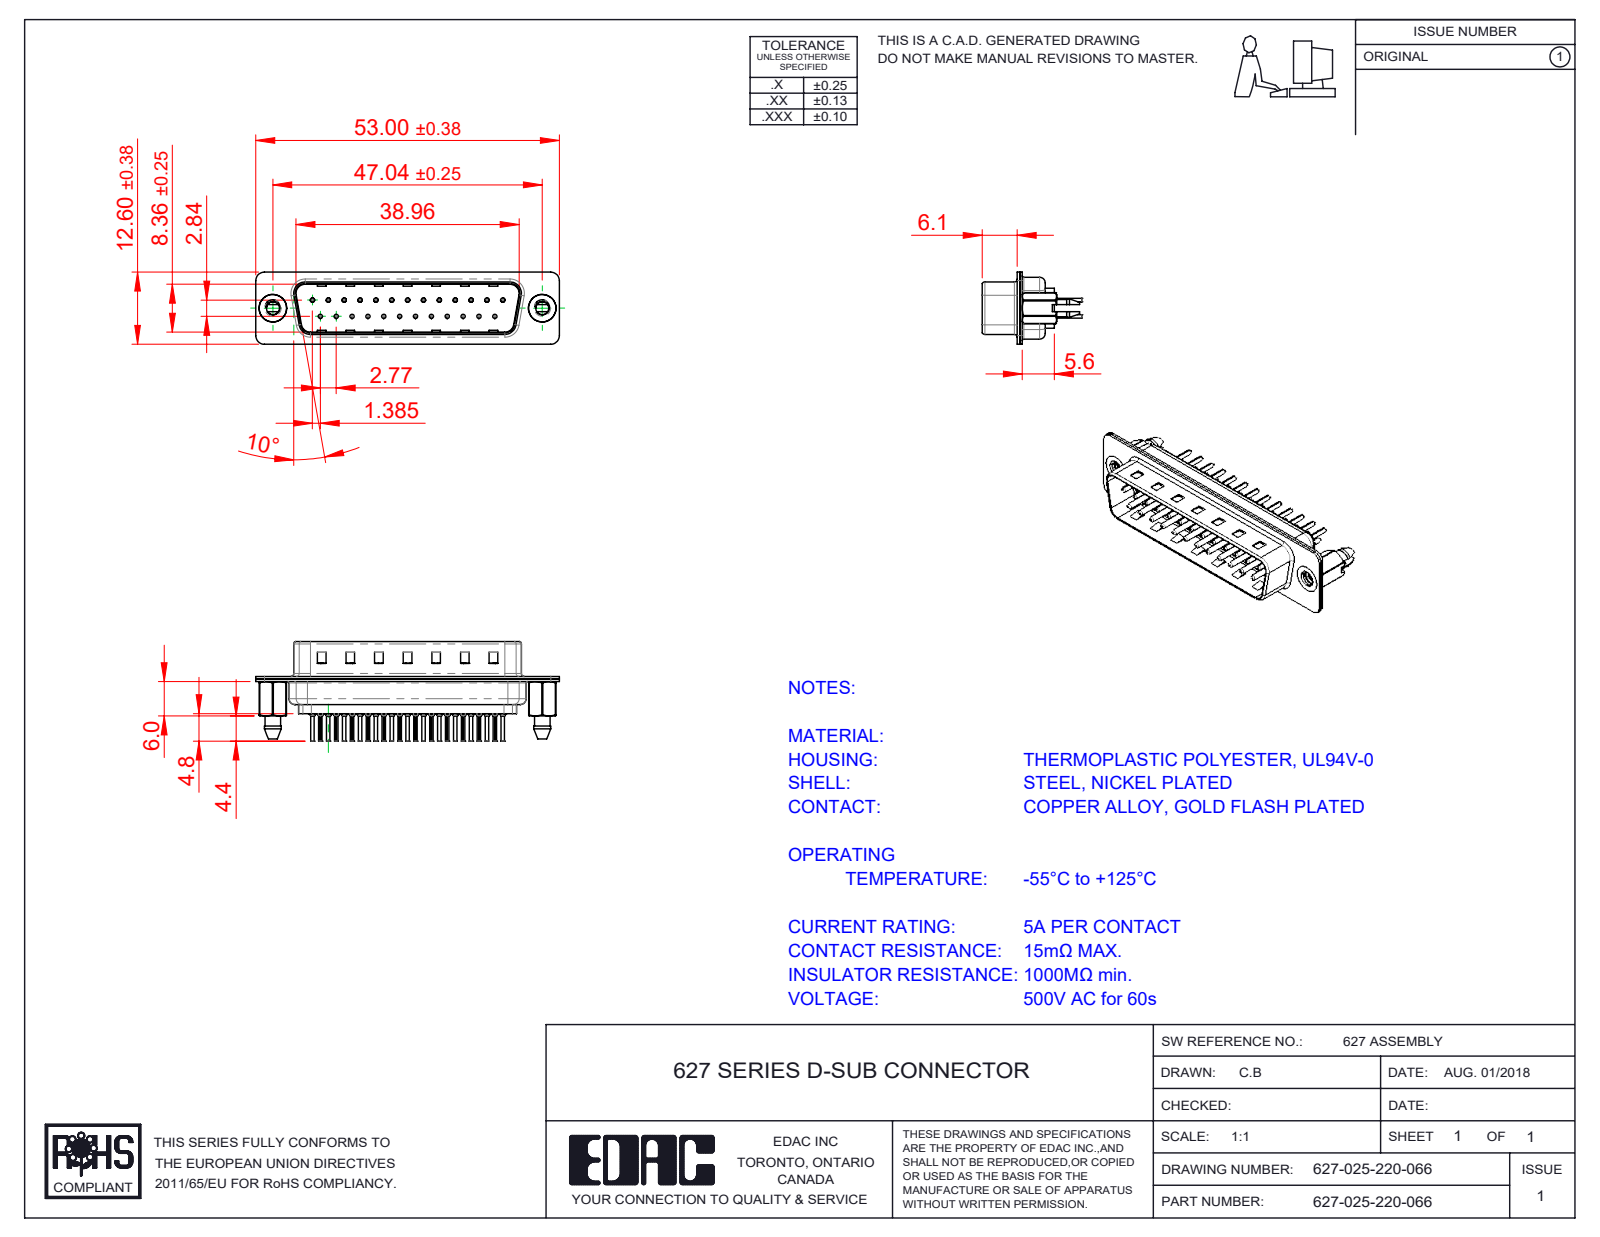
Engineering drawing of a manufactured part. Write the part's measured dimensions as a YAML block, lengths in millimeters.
part_name: "627 4-40 Threaded Boardlock_LP; 627 Contact Row 1_20L; 627-025-220-066; 627 Contact Row 2_20L (+3 more)"
step_written_by: "SolidWorks 2020 (CONFIG_CONTROL_DESIGN)"
units: millimeters
bodies: {solids: 30, faces: 2900, planar: 803, cylindrical: 1094, other: 1003}
overall_size: [53, 17.3, 12.6]
volume: 2797
surface_area: 8096
round_holes:
  - {diameter: 0.2, count: 25}
  - {diameter: 0.35, count: 25}
  - {diameter: 1.1, count: 25}
  - {diameter: 1.6, count: 25}
  - {diameter: 2.26, count: 2}
  - {diameter: 4, count: 2}
  - {diameter: 4.8, count: 2}
round_bosses_or_shafts:
  - {diameter: 2, count: 25}
  - {diameter: 1.5, count: 25}
  - {diameter: 0.75, count: 25}
  - {diameter: 0.6, count: 25}
  - {diameter: 4.9, count: 2}
partial_cylinders:
  - {radius: 0.1, count: 50}
  - {radius: 1.5, count: 18}
  - {radius: 2, count: 12}
  - {radius: 1.6, count: 10}
  - {radius: 0.5, count: 8}
  - {radius: 0.25, count: 4}
  - {radius: 0.6, count: 4}
  - {radius: 0.65, count: 4}
face_to_face_distances: [0.4, 0.45, 0.82, 9.58, 8.76, 0.9, 1.5, 1.4, 6.5, 6.05]
hole_center_spacings: [3.16, 8.31, 2.77, 5.54, 11.08, 16.62, 5.03, 5.04]
